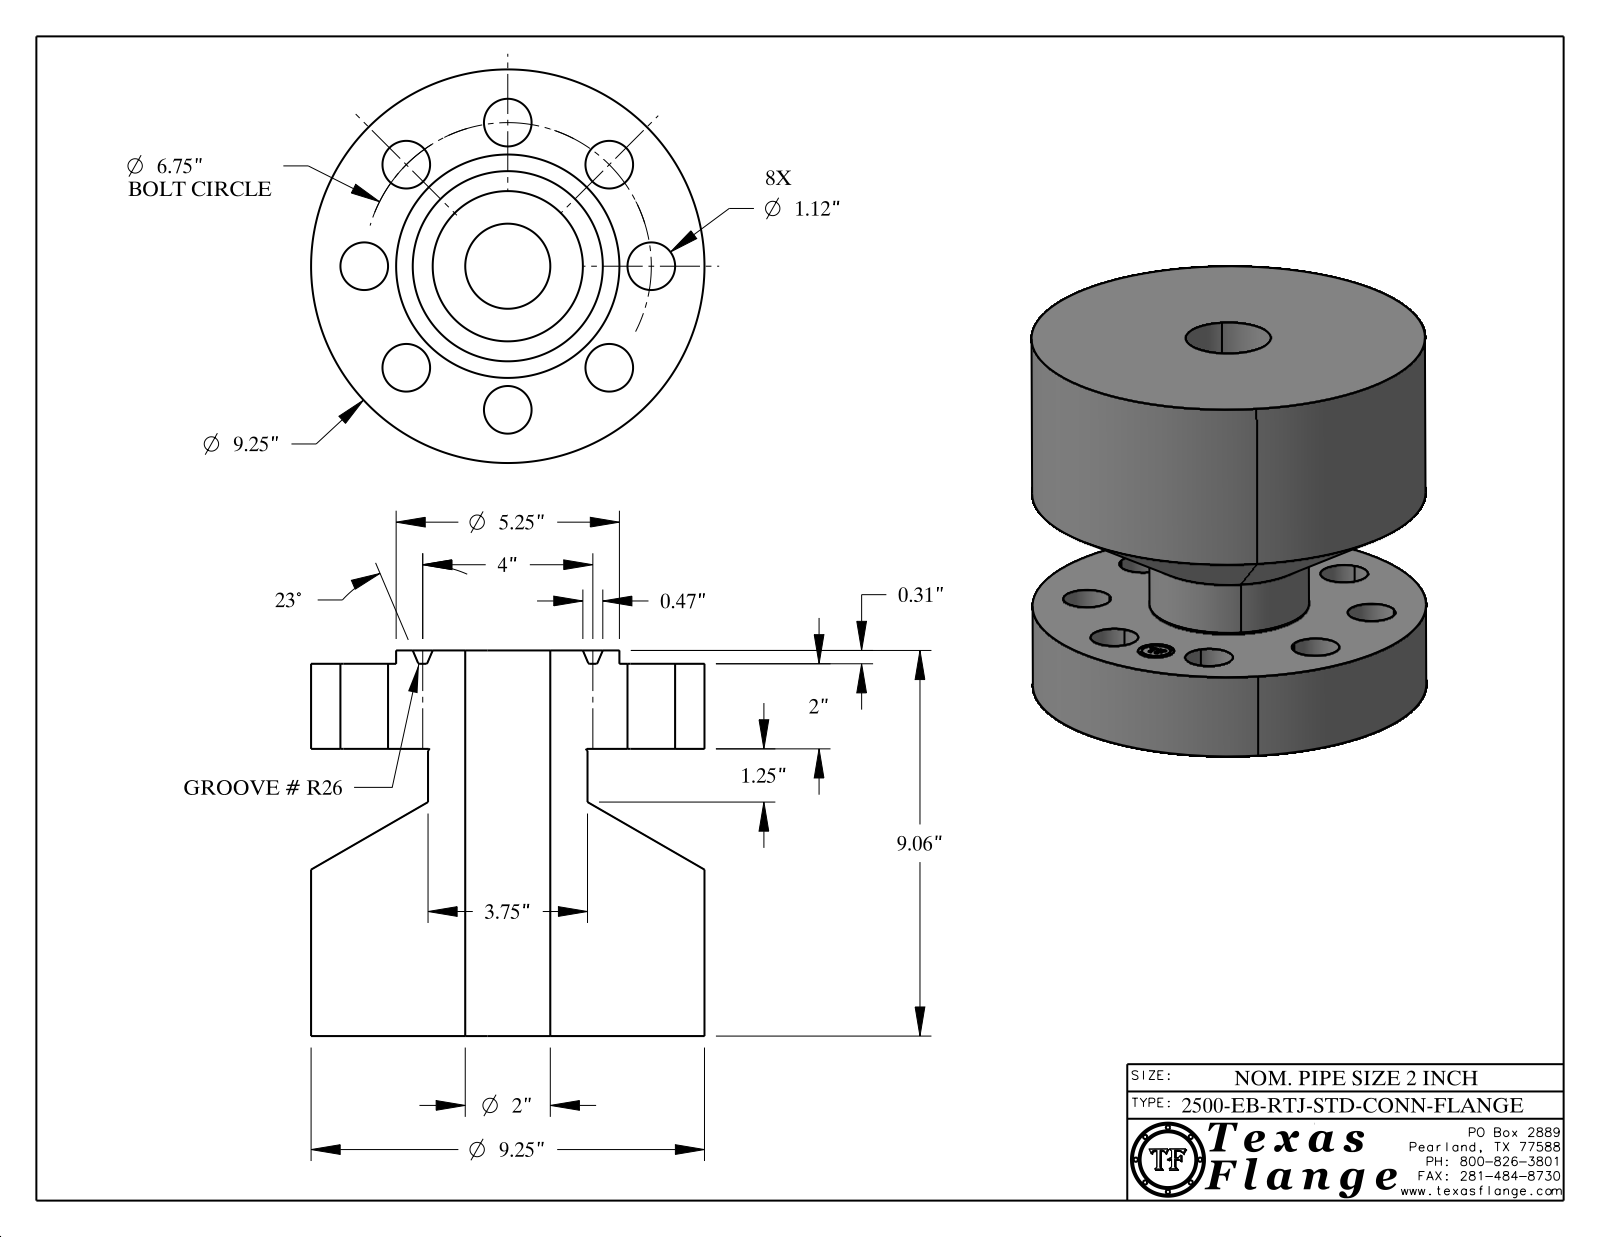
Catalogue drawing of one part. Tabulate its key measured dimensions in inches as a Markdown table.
| quantity | value |
| --- | --- |
| part name | 2-2500-EB-RTJ-STD-CONN-FLANGE |
| STEP written by | CATIA V5 STEP AP214 (AUTOMOTIVE_DESIGN) |
| units | inches |
| bodies | 1 solid, 431 faces (371 planar, 46 cylindrical, 14 other) |
| overall size | 9.25 × 9.25 × 9.063 |
| volume | 428.2 in³ |
| surface area | 543.9 in² |
| round holes (diameter × count) | 1.12 × 8, 0.85 × 1, 2 × 1 |
| round bosses / shafts (diameter × count) | 0.051 × 8, 9.25 × 1, 5.25 × 1, 3.75 × 1, 0.67 × 1 |
| main face-to-face distances | 6.75, 2, 8.75, 0.313, 2.313, 9.063, 2.308, 1.995, 6.755, 0.254 |
| hole center spacings | 3.375, 2.583, 4.773, 6.237, 6.75, 1.317, 5.613, 6.62 |
